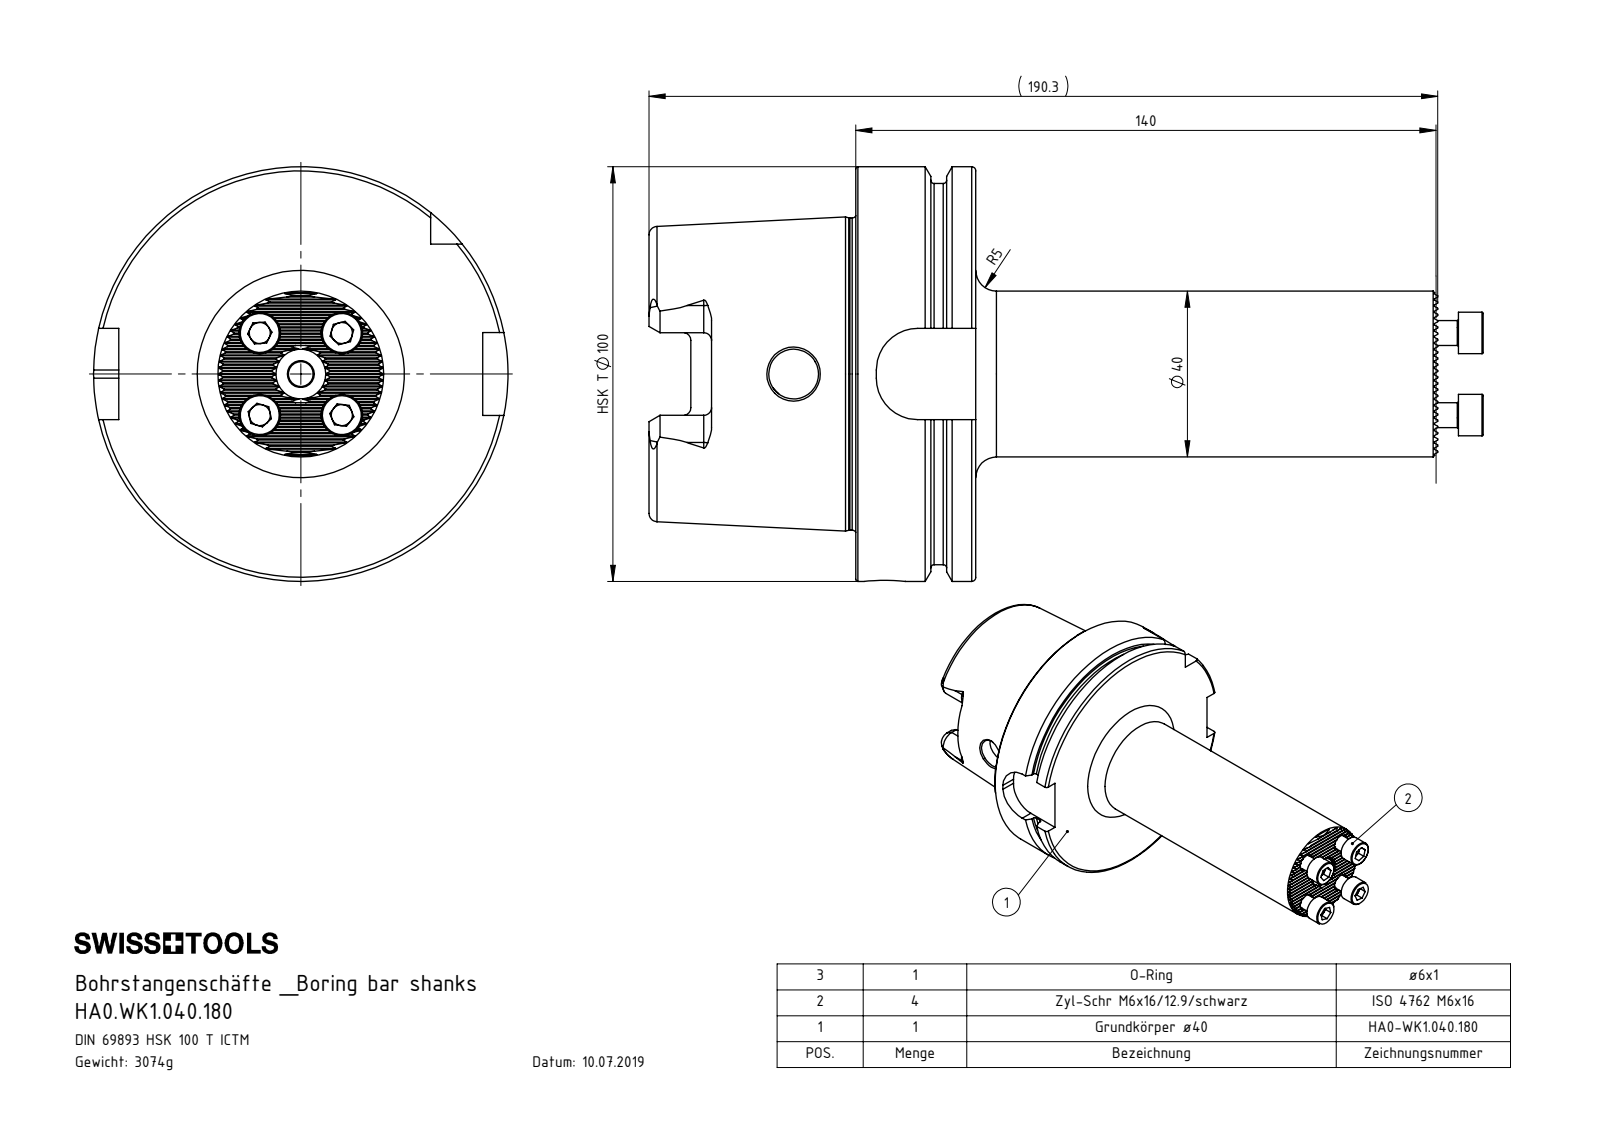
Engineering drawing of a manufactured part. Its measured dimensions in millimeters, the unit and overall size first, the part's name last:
Units: millimetres
Overall size (bounding box): 201.3 × 100 × 100
Round holes (diameter × count): ⌀5 ×4, ⌀6 ×1, ⌀6.8 ×1, ⌀7.4 ×1, ⌀10 ×1, ⌀12 ×1, ⌀22.5 ×1, ⌀26 ×1, ⌀53 ×1, ⌀63 ×1
Round bosses / shafts (diameter × count): ⌀10 ×3, ⌀6 ×3, ⌀100 ×1, ⌀91.95 ×1, ⌀75.26 ×1, ⌀40 ×1
Partial cylindrical surfaces — rounded edges, fillets, slot ends (radius × count): R0.12 ×27, R1.9 ×6, R4.88 ×4, R10 ×4
Main face-to-face distances: 28.95, 12.45, 16.5, 49.9, 62.35, 78.85, 1.3, 2.6, 3.9, 5.2
Hole centre spacings: 14, 19.8, 28
Volume: 390 610 mm³ · Surface area: 69 365 mm²
Bodies: 5 solids, 412 faces (247 planar, 97 cylindrical, 68 other)
Part name (STEP PRODUCT): HA0-WK1.040.180_A; ISO 4762 - M6 x 16; DIN 3771 - 6x1; HA0.WK1.040.180
STEP written by: SolidWorks 2017 (AUTOMOTIVE_DESIGN)
